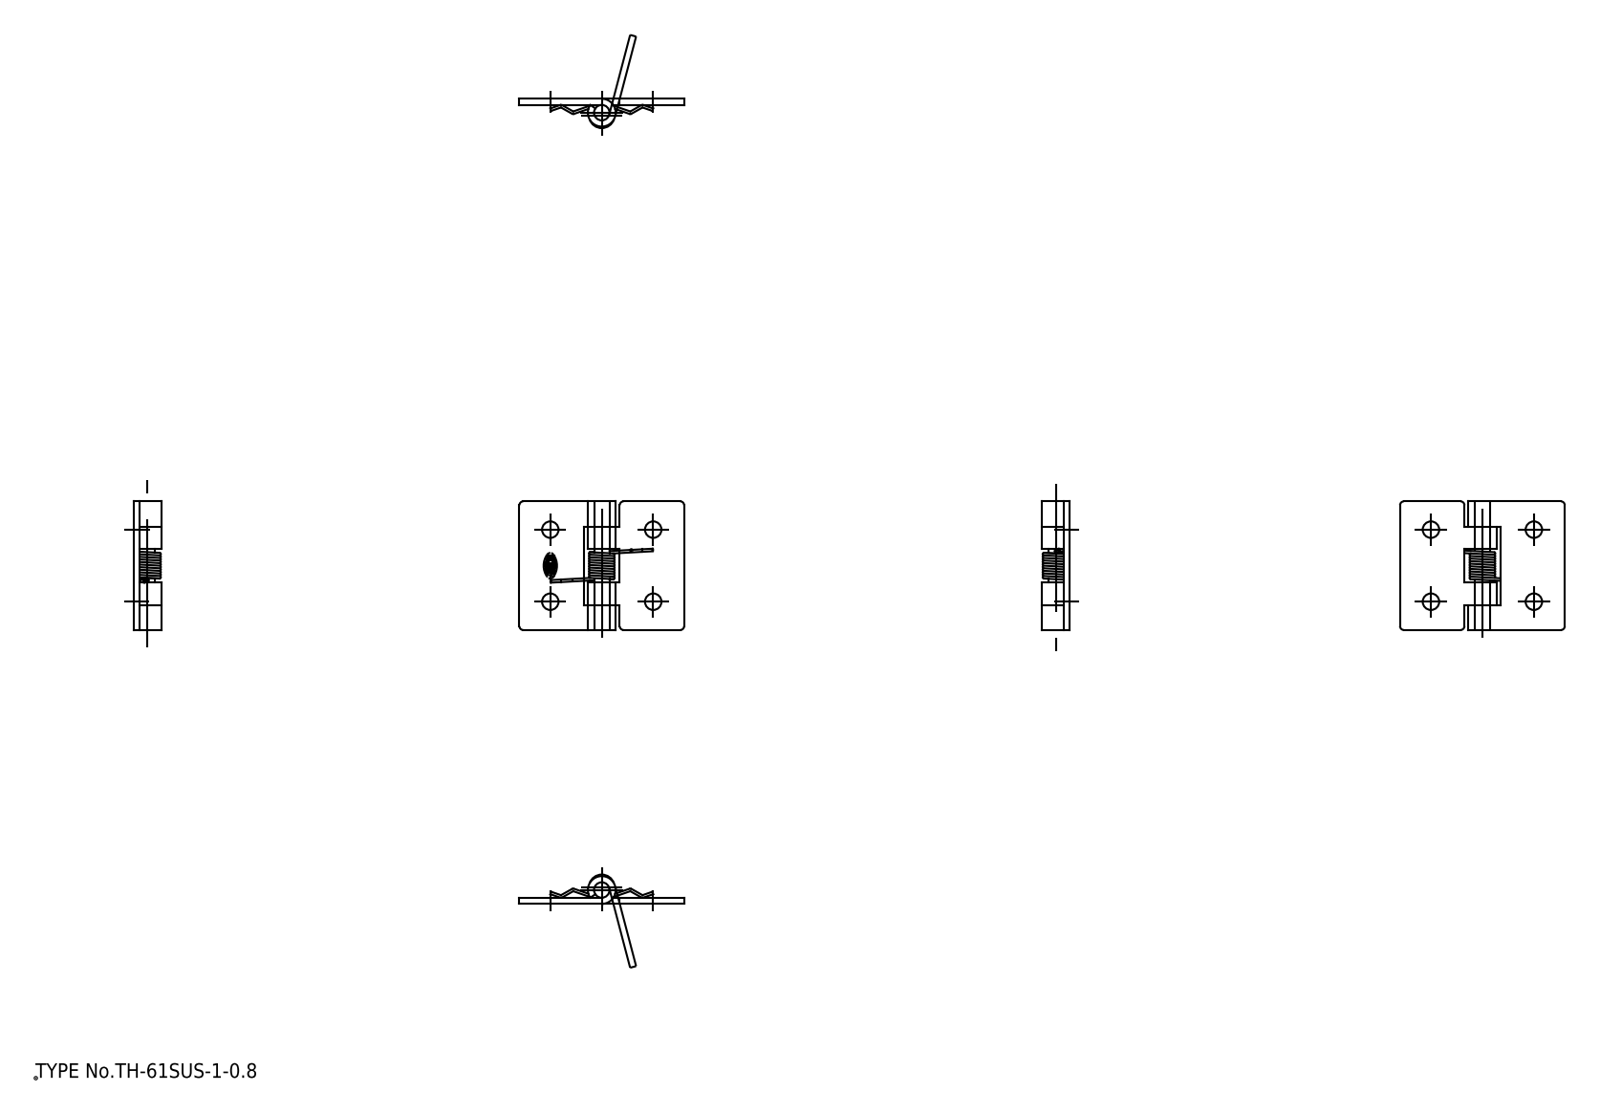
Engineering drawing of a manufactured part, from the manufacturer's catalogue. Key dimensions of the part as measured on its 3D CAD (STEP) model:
Part name (STEP PRODUCT): shaft; hinge piece_B; hinge piece_A; spring
STEP written by: spGate 19.8.4 (****-****-****-****) (AUTOMOTIVE_DESIGN)
Units: millimetres
Bodies: 4 solids, 70 faces (28 planar, 24 cylindrical, 18 other)
Overall size (bounding box): 32 × 25 × 5.4
Volume: 1 242 mm³ · Surface area: 2 590 mm²
Round holes (diameter × count): ⌀3.2 ×4, ⌀3 ×1
Round bosses / shafts (diameter × count): ⌀5.4 ×1
Partial cylindrical surfaces — rounded edges, fillets, slot ends (radius × count): R0.75 ×6
Main face-to-face distances: 1.2, 4.9, 20.1, 25, 12.5, 19.5, 9.25, 15.75, 4.35, 10.85
Hole centre spacings: 14, 20, 24.41
